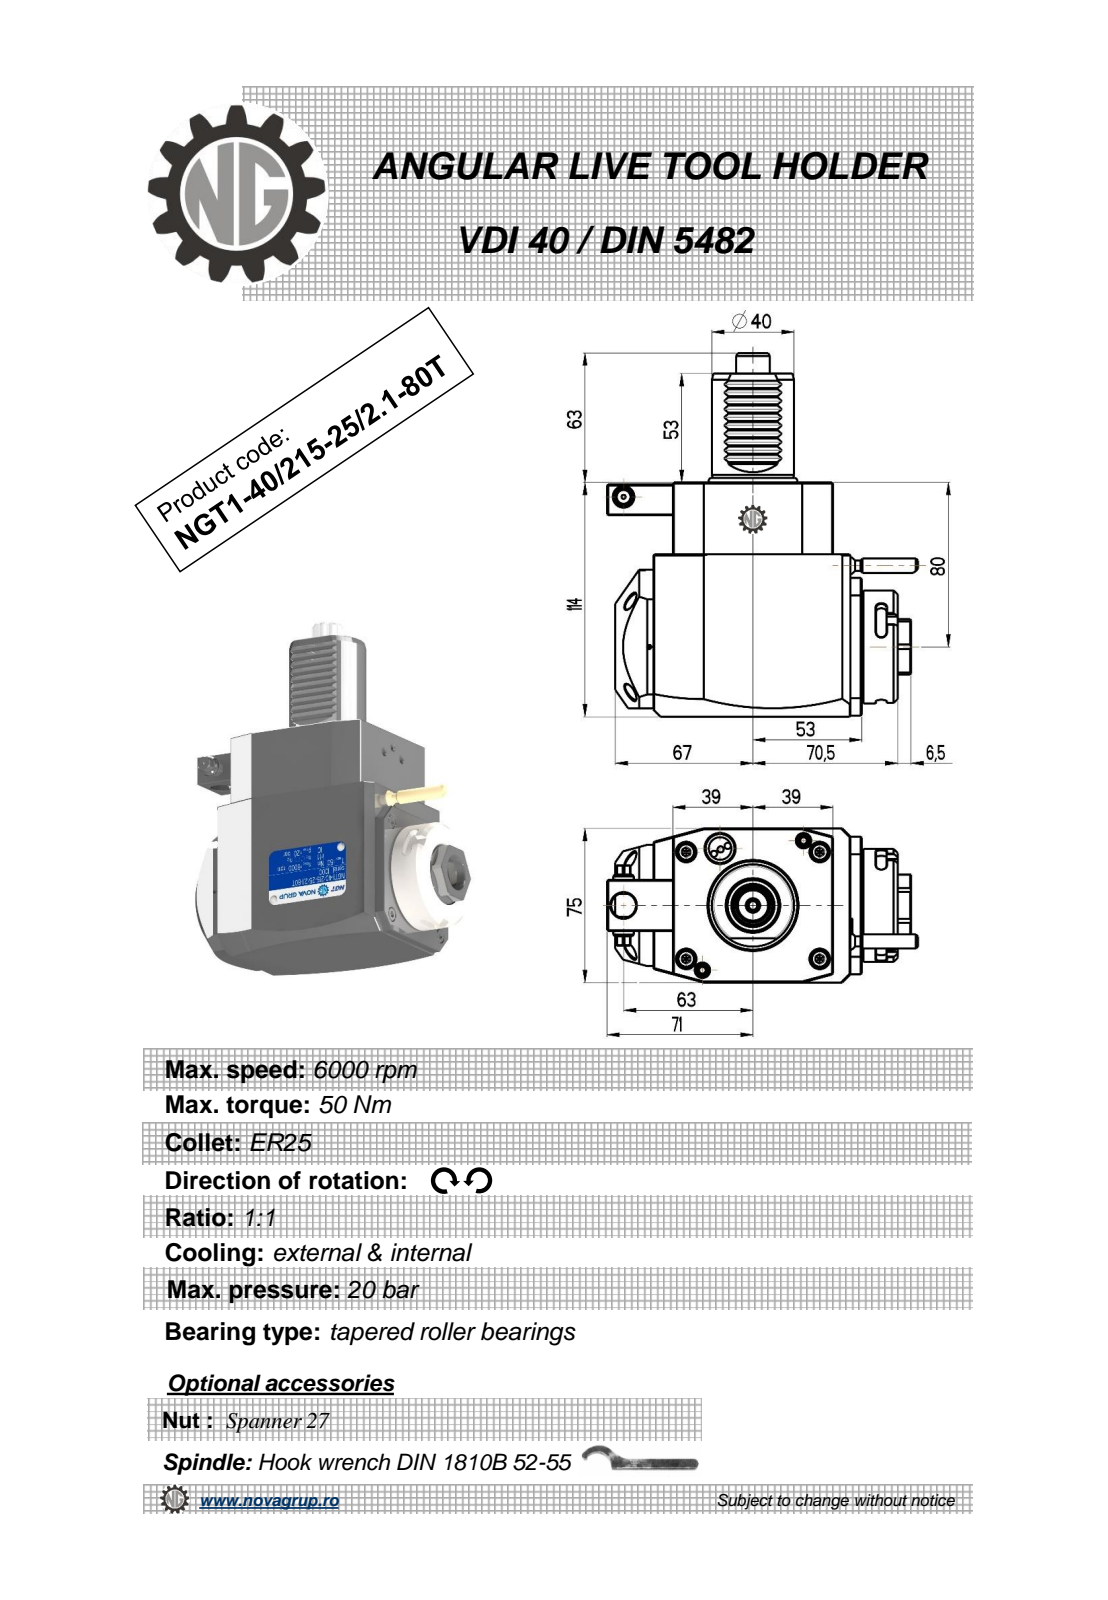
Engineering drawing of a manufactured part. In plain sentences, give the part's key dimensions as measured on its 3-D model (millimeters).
The part is named "NGT1_40_215_25_1_1_80T". Its 3-D file was written by "PRO/ENGINEER BY PARAMETRIC TECHNOLOGY CORPORATION, 2010280 (CONFIG_CONTROL_DESIGN)". It is 1 solid with 397 faces: 177 planar, 127 cylindrical and 93 other. Overall it measures 177 by 151.33 by 75 millimeters. Its volume is 946 941 cubic millimeters and its surface area 70 342 square millimeters. Round holes: 1 of diameter 2, 1 of diameter 2.5, 1 of diameter 3, 1 of diameter 4.2, 1 of diameter 4.5, 1 of diameter 5.3, 1 of diameter 9.5, 1 of diameter 12, 1 of diameter 18. Round bosses or shafts: 2 of diameter 8, 1 of diameter 55, 1 of diameter 48, 1 of diameter 40, 1 of diameter 10, 1 of diameter 7, 1 of diameter 5, 1 of diameter 4. Partial cylindrical surfaces (rounded edges, fillets, slot ends): 18 of radius 3.03, 10 of radius 0.3, 6 of radius 2.5, 2 of radius 180, 1 of radius 0.5, 1 of radius 3.85, 1 of radius 4.25, 1 of radius 6.75. The main face-to-face distances are 75, 114, 14, 17.5, 78, 92, 109.5, 31.5, 4, 28. The hole center spacings are 37.35, 43.2, 63, 72.5.
